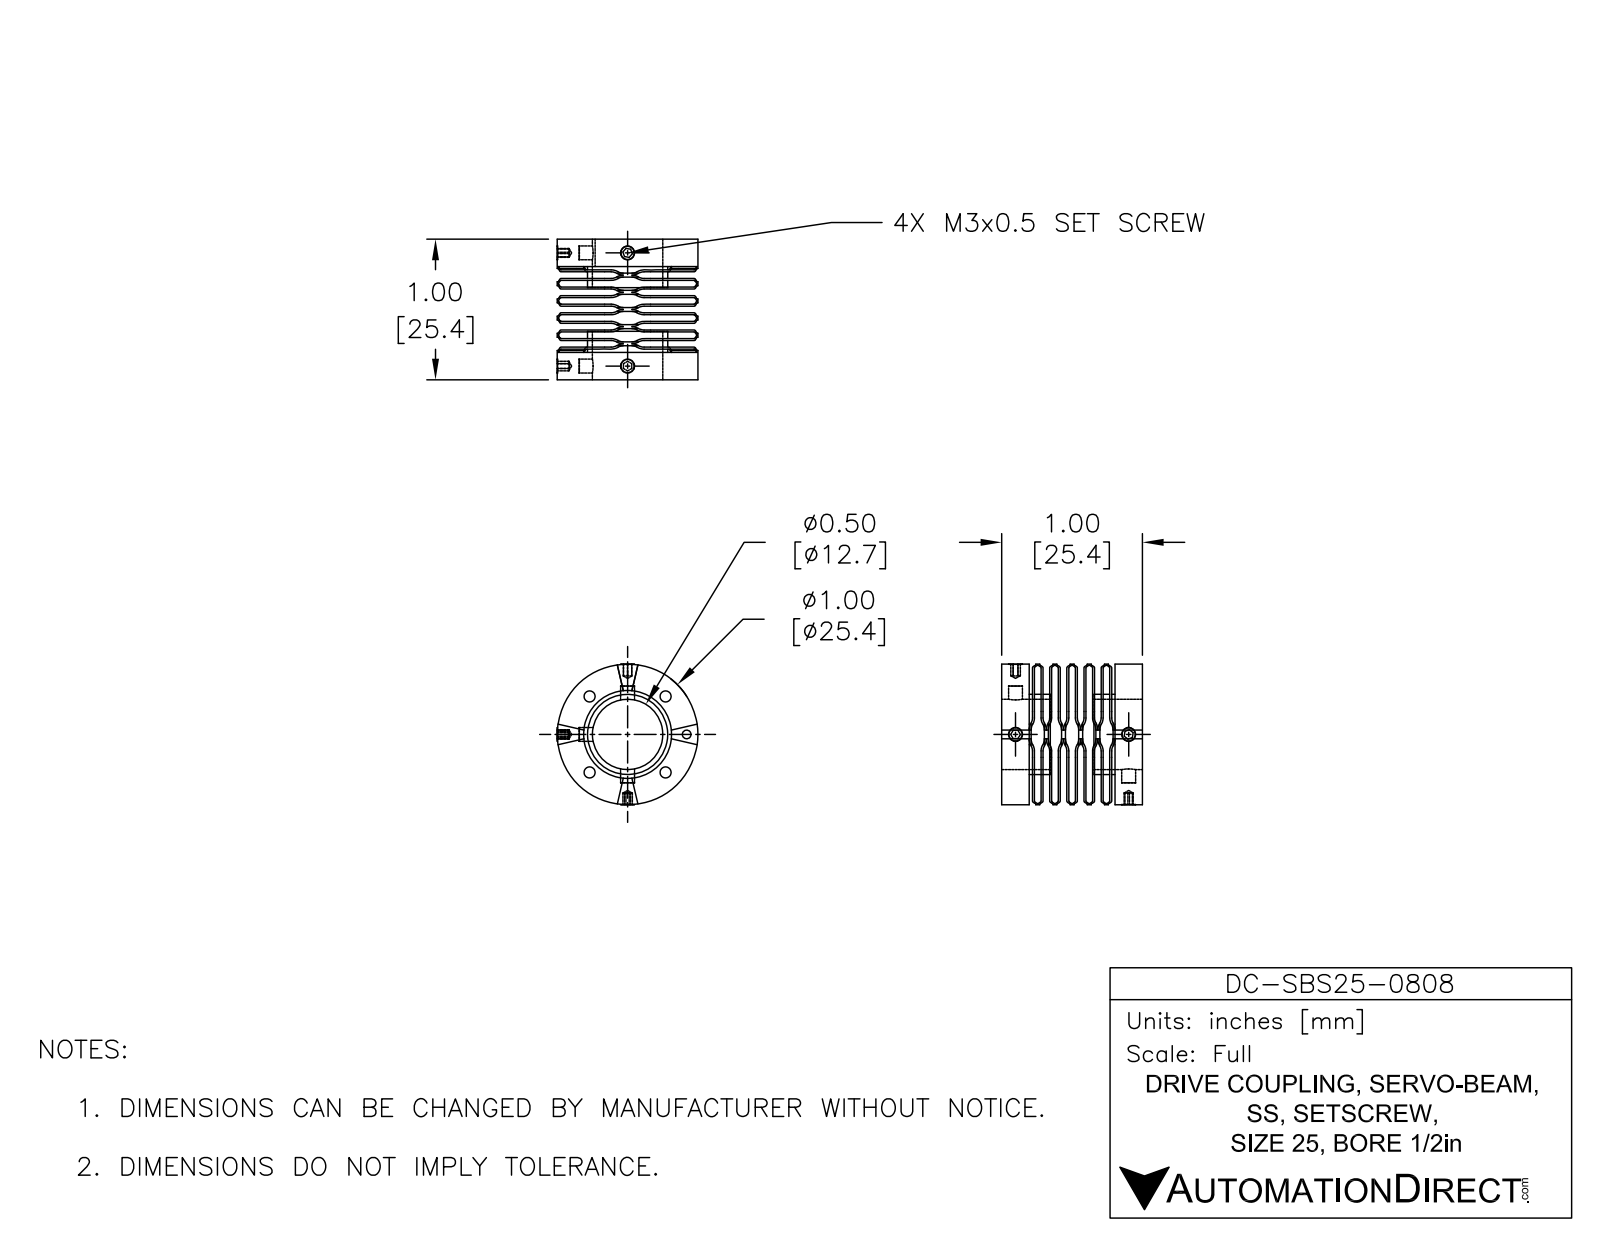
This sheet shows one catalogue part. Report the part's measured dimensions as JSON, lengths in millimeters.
{"part_name": "DC-SBS25-0808", "step_written_by": "SolidWorks 2015 (AUTOMOTIVE_DESIGN)", "units": "millimeters", "bodies": {"solids": 16, "faces": 878, "planar": 362, "cylindrical": 508, "other": 8}, "overall_size": [26, 25.7, 23.4], "volume_mm3": 4844, "surface_area_mm2": 10466, "round_holes": [[1.99, 4], [2.2, 4], [1.57, 1], [12.7, 1], [15.87, 1]], "round_bosses_or_shafts": [[2.5, 3], [25.4, 1], [14.48, 1], [2.39, 1]], "partial_cylinders_radius": [[0.7, 320]], "face_to_face_distances": [2.7, 1.2, 0.9, 5.4, 1.5, 1.8, 3.6, 3.9, 6.3, 4.5], "hole_center_spacings": [9.7, 13.72, 7.85, 18.82, 19.4, 10.67, 19.32]}
